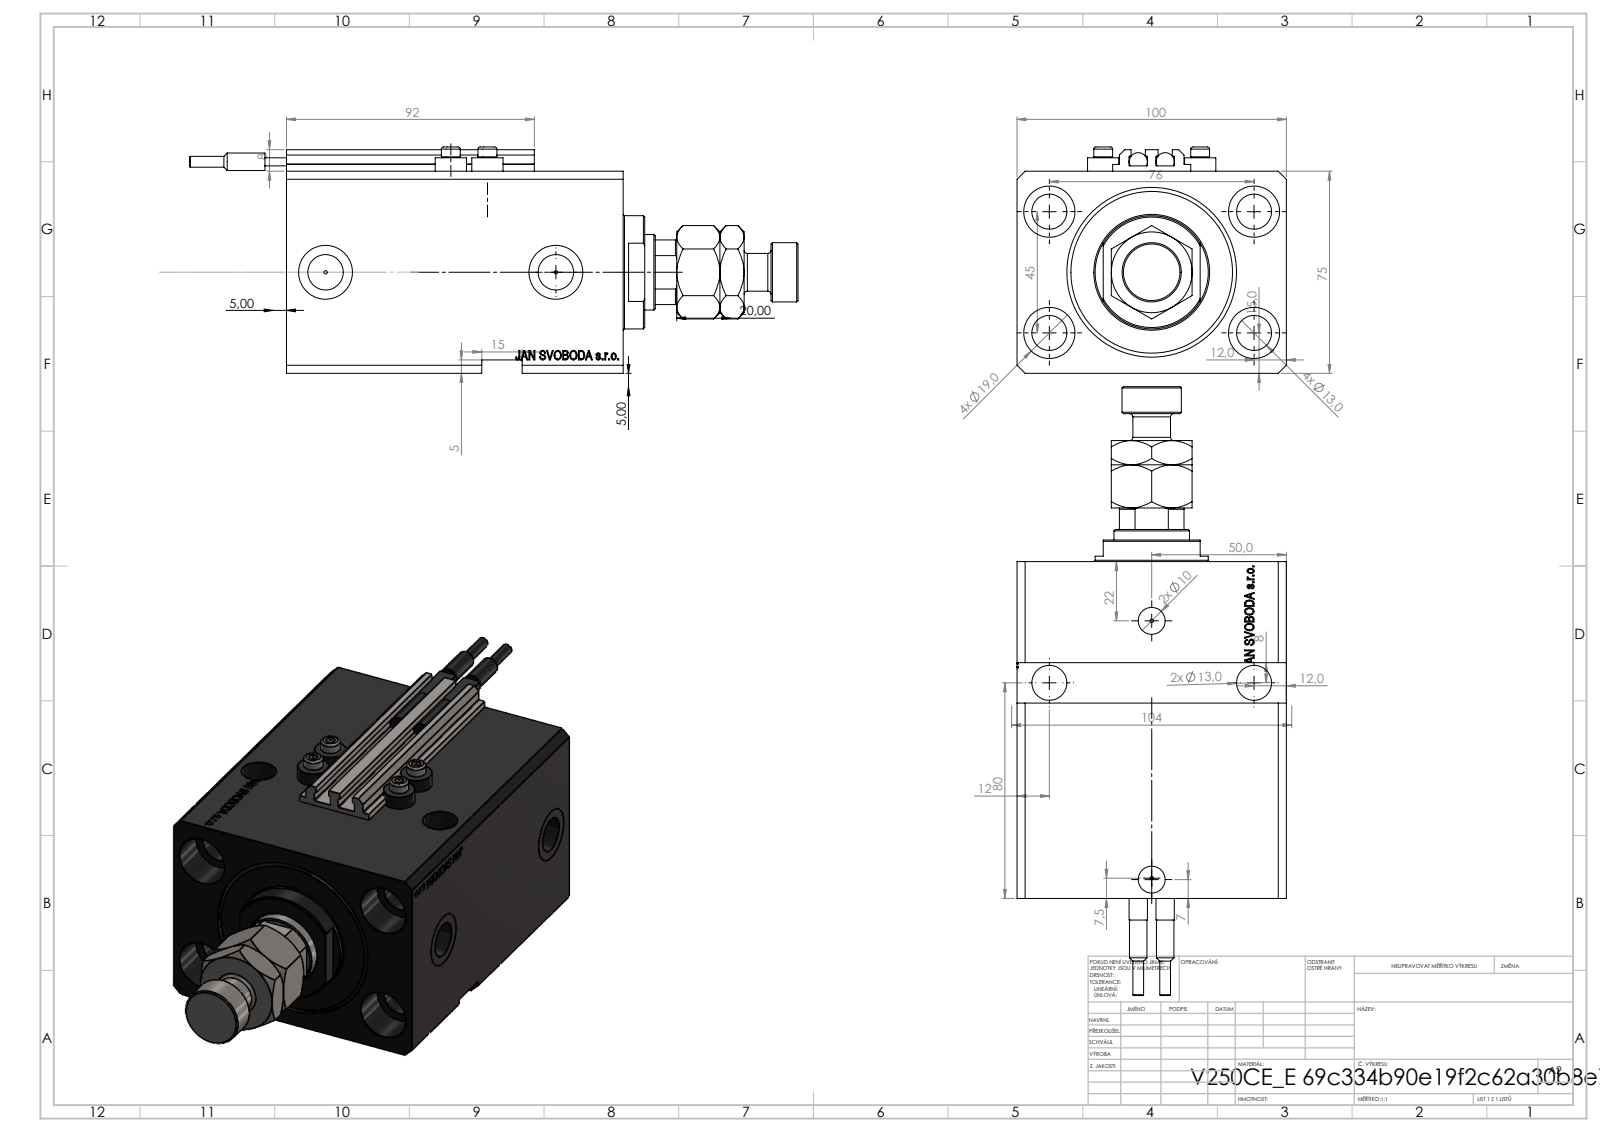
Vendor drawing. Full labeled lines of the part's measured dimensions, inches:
Part name (STEP PRODUCT): MFA; V250CE_E; SWITCH_V250CE; V250CE_VC_E (+2 more)
STEP written by: SolidWorks 2019 (CONFIG_CONTROL_DESIGN)
Units: inches
Bodies: 11 solids, 1208 faces (587 planar, 154 cylindrical, 467 other)
Overall size (bounding box): 8.894 × 3.937 × 3.307
Volume: 49.27 in³ · Surface area: 245.8 in²
Round holes (diameter × count): ⌀0.512 ×6, ⌀0.049 ×4, ⌀0.157 ×4, ⌀0.748 ×4, ⌀0.394 ×2, ⌀0.518 ×2, ⌀0.787 ×2, ⌀0.728 ×1, ⌀1.102 ×1, ⌀1.969 ×1, ⌀2.48 ×1
Round bosses / shafts (diameter × count): ⌀0.457 ×4, ⌀0.276 ×4, ⌀0.268 ×2, ⌀0.256 ×2, ⌀0.157 ×2, ⌀1.654 ×1, ⌀0.866 ×1, ⌀0.551 ×1
Partial cylindrical surfaces — rounded edges, fillets, slot ends (radius × count): R0.008 ×10, R0.531 ×1
Main face-to-face distances: 2.953, 3.937, 4.921, 0.469, 4.453, 3.874, 3.406, 1.047, 0.118, 1.906
Hole centre spacings: 1.739, 2.992, 0.535, 0.816, 1.086, 1.324, 1.417, 1.515
